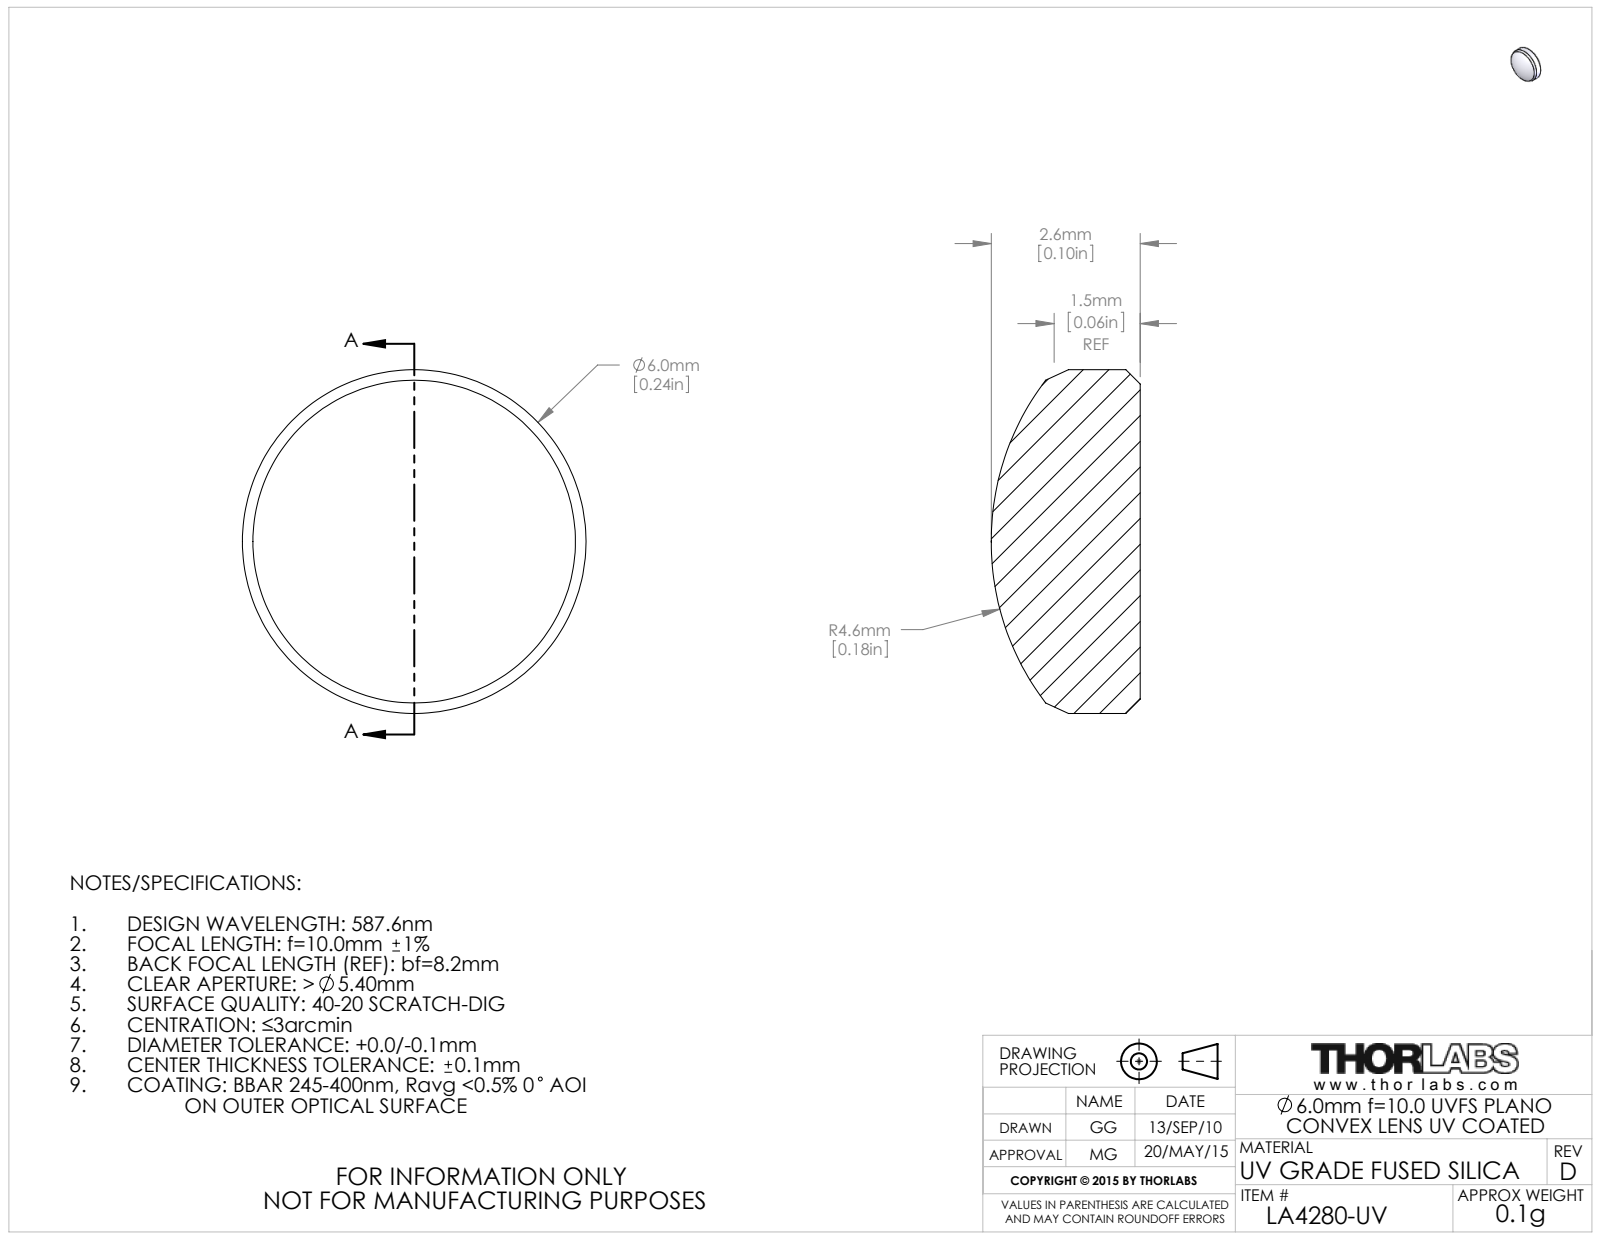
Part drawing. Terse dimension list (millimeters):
name: 4268-E0W
written by: SolidWorks 2014 (CONFIG_CONTROL_DESIGN)
unit: mm
bodies: 1 solid, 9 faces (1 planar, 2 cylindrical, 6 other)
size: 6 × 6 × 2.6
volume: 58 mm³; area: 85 mm²
bosses: 1× ⌀6
